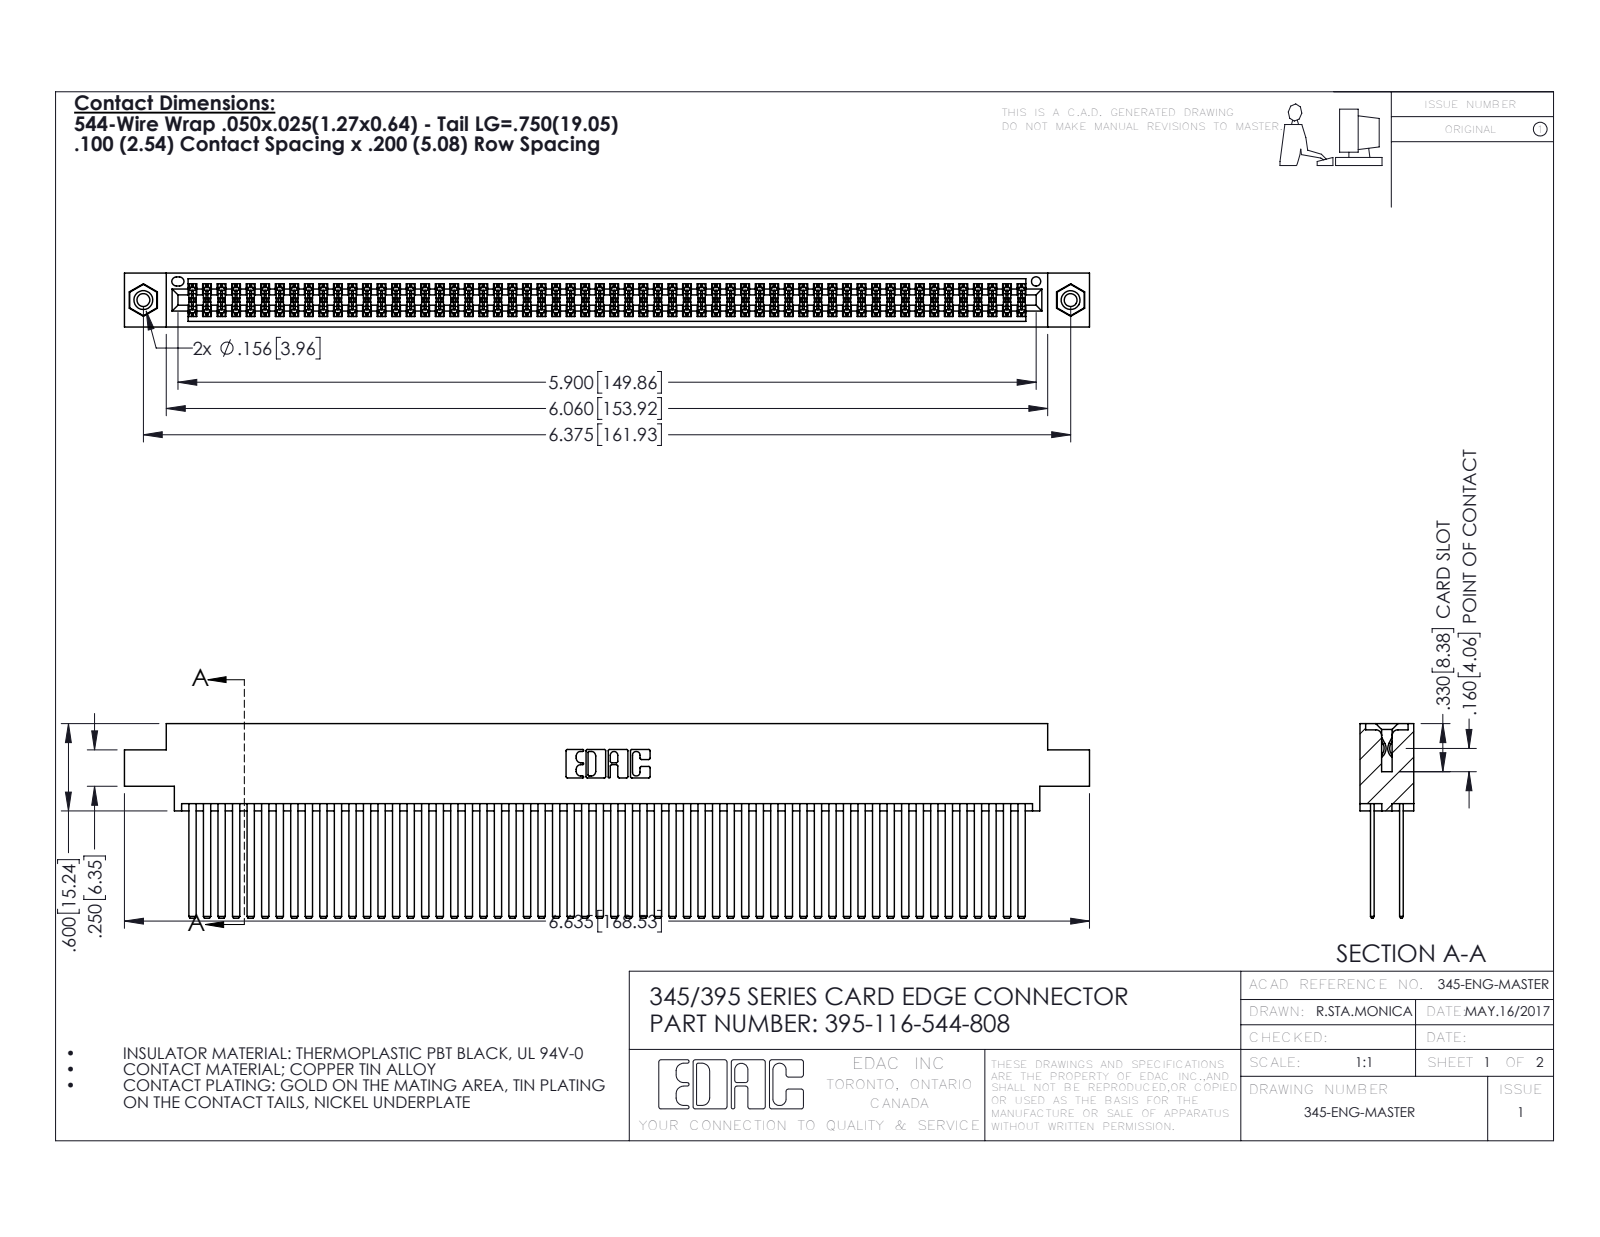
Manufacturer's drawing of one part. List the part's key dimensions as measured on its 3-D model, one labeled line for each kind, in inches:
Part name (STEP PRODUCT): 395-116-544-808; 345 Part_0.170 Offset - 0.156 Dia-TI; 345-250-001_345-250-003-102; 345-292-001_345-293-144
STEP written by: SolidWorks 2016 (CONFIG_CONTROL_DESIGN)
Units: inches
Bodies: 119 solids, 5294 faces (3480 planar, 1798 cylindrical, 16 other)
Overall size (bounding box): 6.635 × 1.337 × 0.37
Volume: 1.1 in³ · Surface area: 49.41 in²
Round holes (diameter × count): ⌀0.089 ×2, ⌀0.125 ×2, ⌀0.156 ×2, ⌀0.064 ×1
Round bosses / shafts (diameter × count): ⌀0.155 ×2
Partial cylindrical surfaces — rounded edges, fillets, slot ends (radius × count): R0.006 ×174, R0.01 ×22, R0.007 ×6, R0.031 ×6, R0.026 ×3, R0.014 ×2, R0.019 ×2, R0.022 ×2
Main face-to-face distances: 0.2, 0.025, 0.072, 0.098, 0.272, 0.298, 0.225, 0.175, 0.37, 0.15
Hole centre spacings: 0.27, 6.139, 6.375
